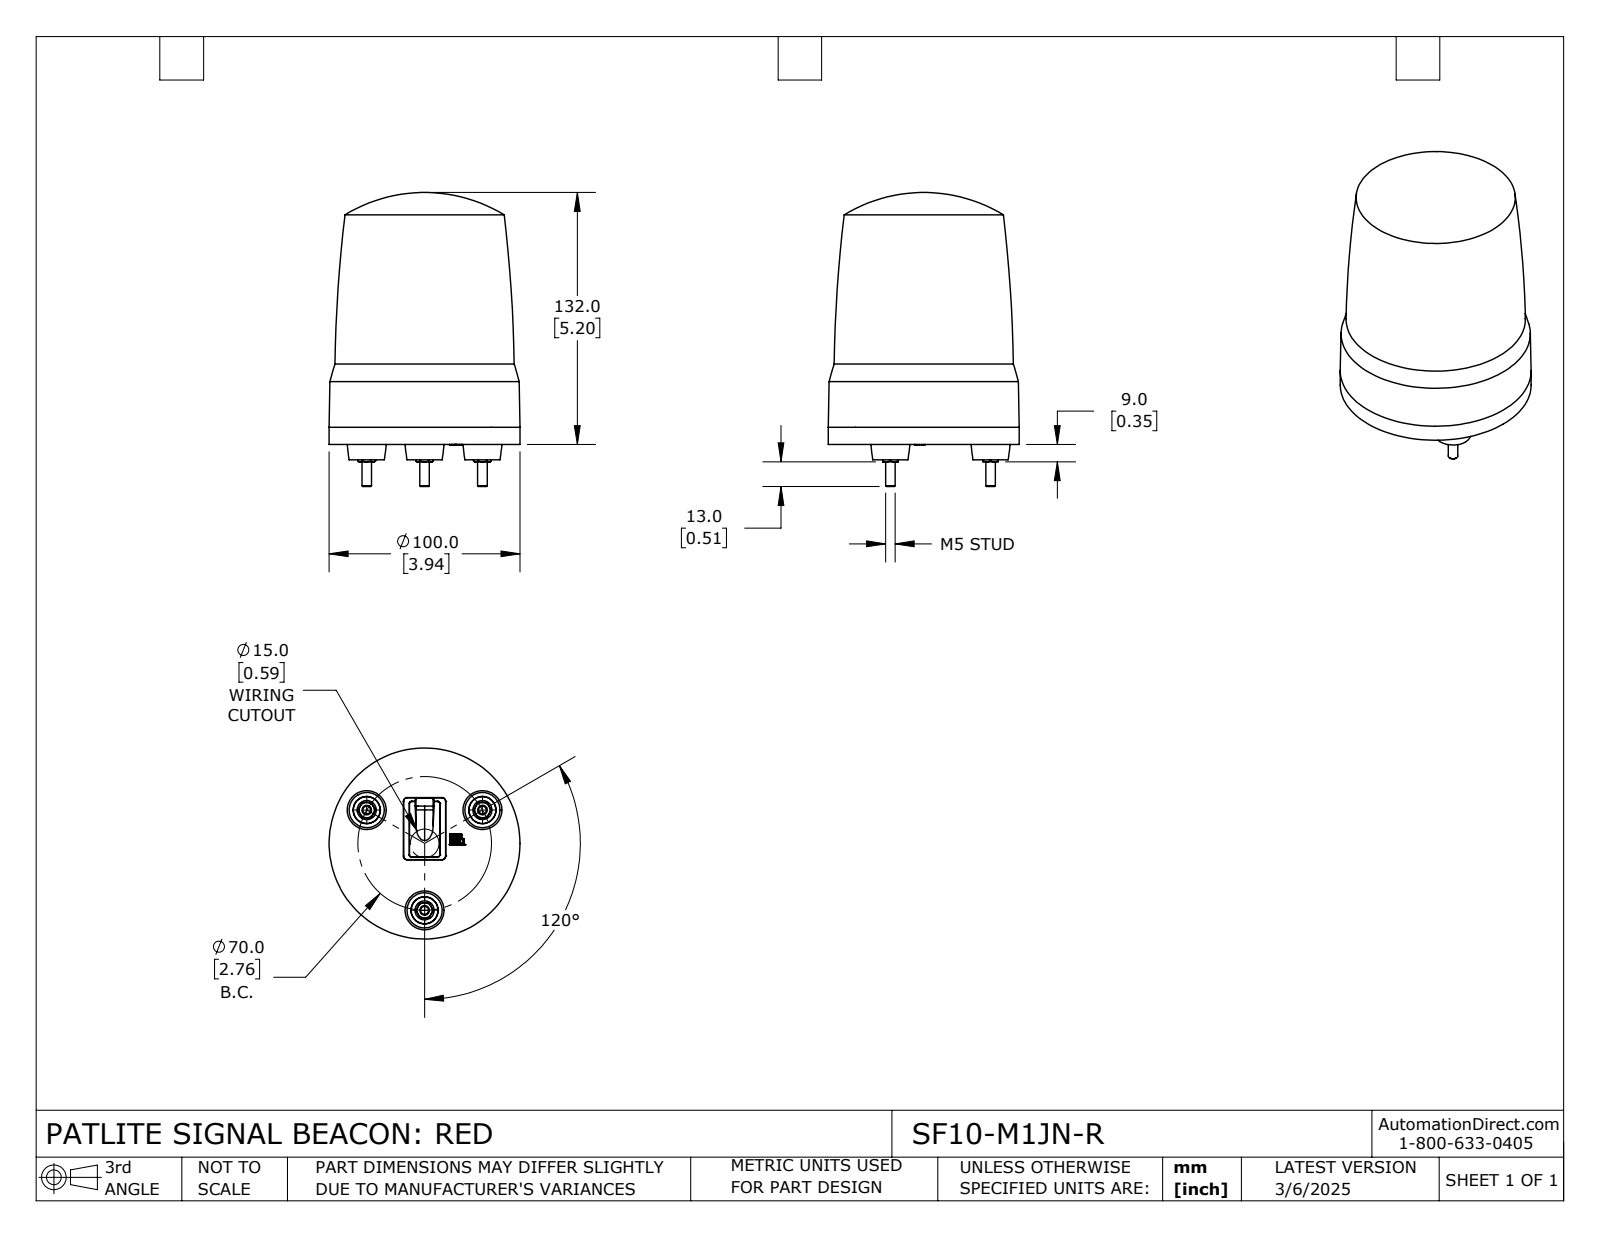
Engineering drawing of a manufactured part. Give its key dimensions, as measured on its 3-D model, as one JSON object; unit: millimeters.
{"part_name": "SF10-M1JN-R", "step_written_by": "SolidWorks 2024 (CONFIG_CONTROL_DESIGN)", "units": "millimeters", "bodies": {"solids": 1, "faces": 327, "planar": 159, "cylindrical": 14, "other": 154}, "overall_size": [154, 100, 100], "volume_mm3": 859960, "surface_area_mm2": 52586, "round_bosses_or_shafts": [[10, 3], [5, 3], [100, 1]], "face_to_face_distances": [8, 0.85, 8.85, 1.6, 10.45, 2.45, 3.8, 4.2, 5.05, 6.65]}
